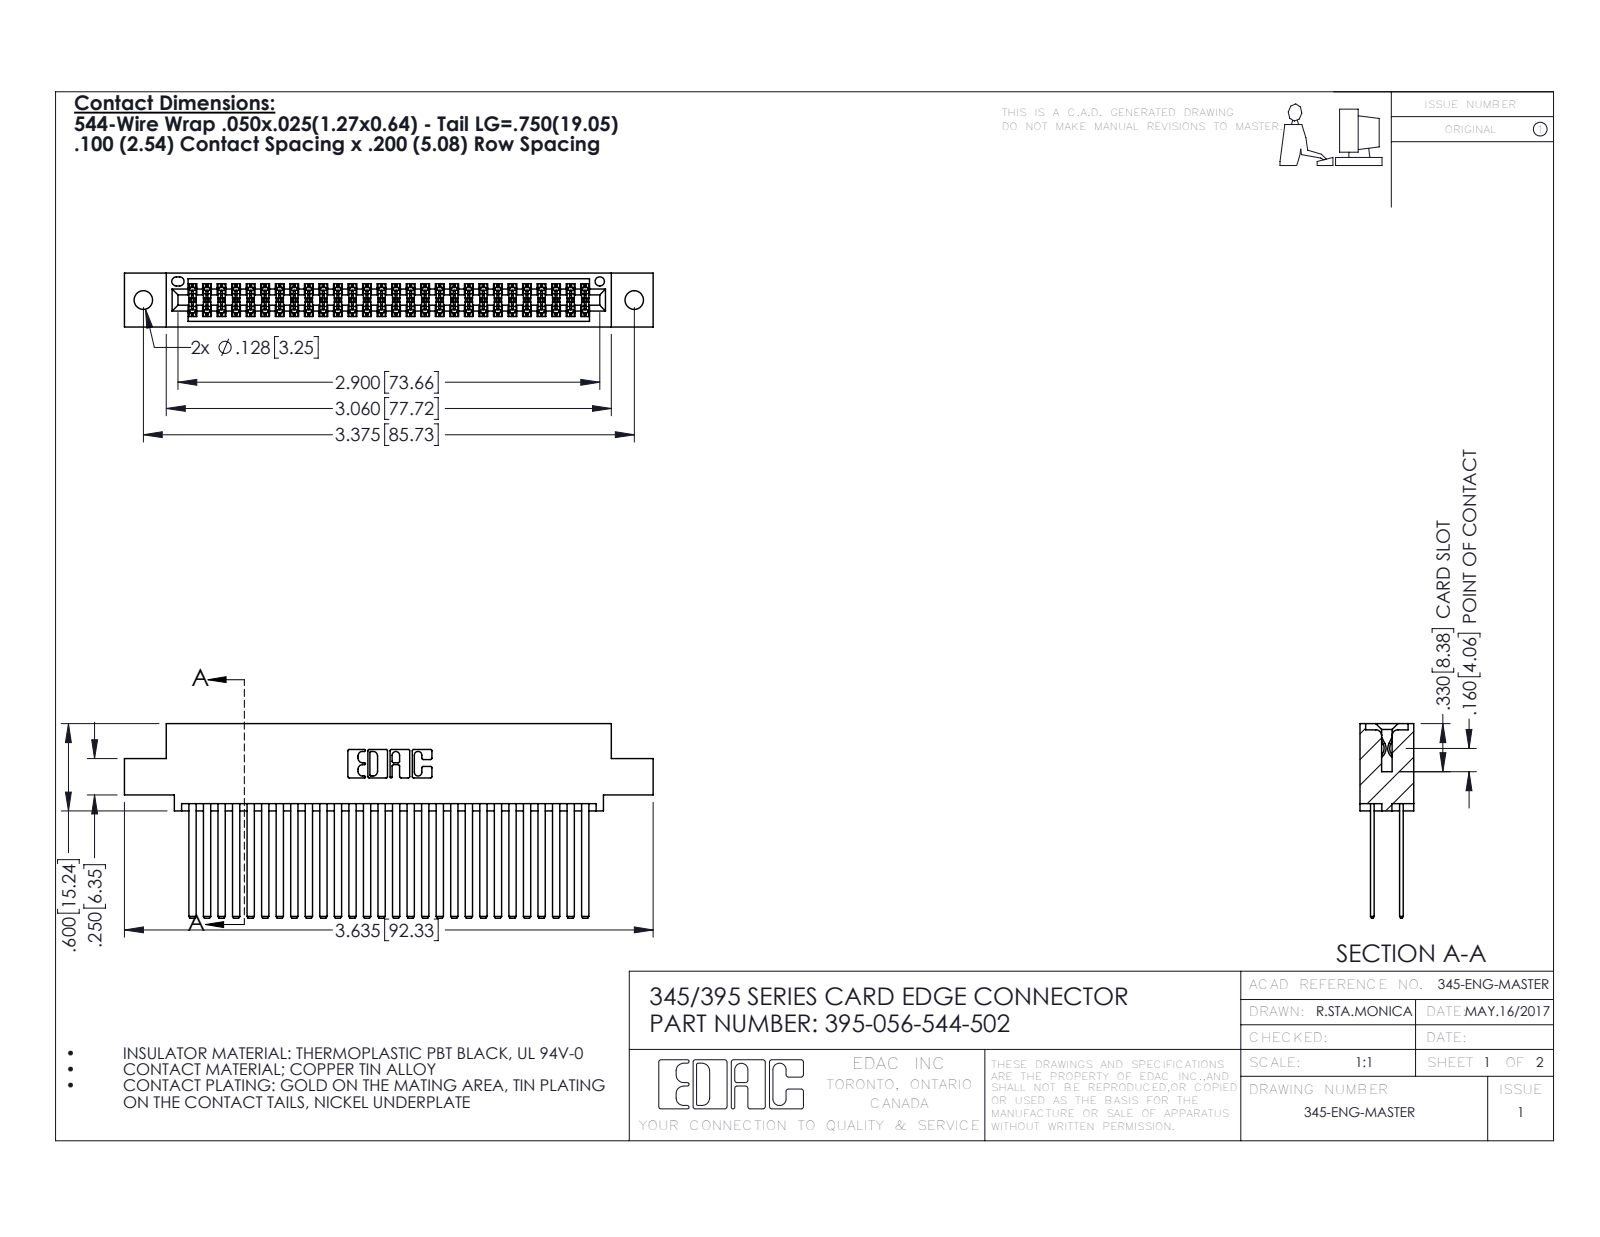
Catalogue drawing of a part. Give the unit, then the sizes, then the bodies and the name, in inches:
Units: inches
Overall size (bounding box): 3.635 × 1.337 × 0.37
Round holes (diameter × count): ⌀0.128 ×2, ⌀0.064 ×1
Partial cylindrical surfaces — rounded edges, fillets, slot ends (radius × count): R0.006 ×84, R0.01 ×22, R0.007 ×6, R0.031 ×6, R0.026 ×3, R0.014 ×2, R0.019 ×2, R0.022 ×2
Main face-to-face distances: 0.2, 0.025, 0.298, 0.072, 0.098, 0.272, 0.225, 0.175, 0.37, 0.05
Hole centre spacings: 0.27, 3.14, 3.375
Volume: 0.581 in³ · Surface area: 24.67 in²
Bodies: 57 solids, 2594 faces (1708 planar, 886 cylindrical, 0 other)
Part name (STEP PRODUCT): 345-292-001_345-293-144; 395-056-544-502; 345 Part_0.110 Offset - 0.128 Dia
STEP written by: SolidWorks 2016 (CONFIG_CONTROL_DESIGN)
